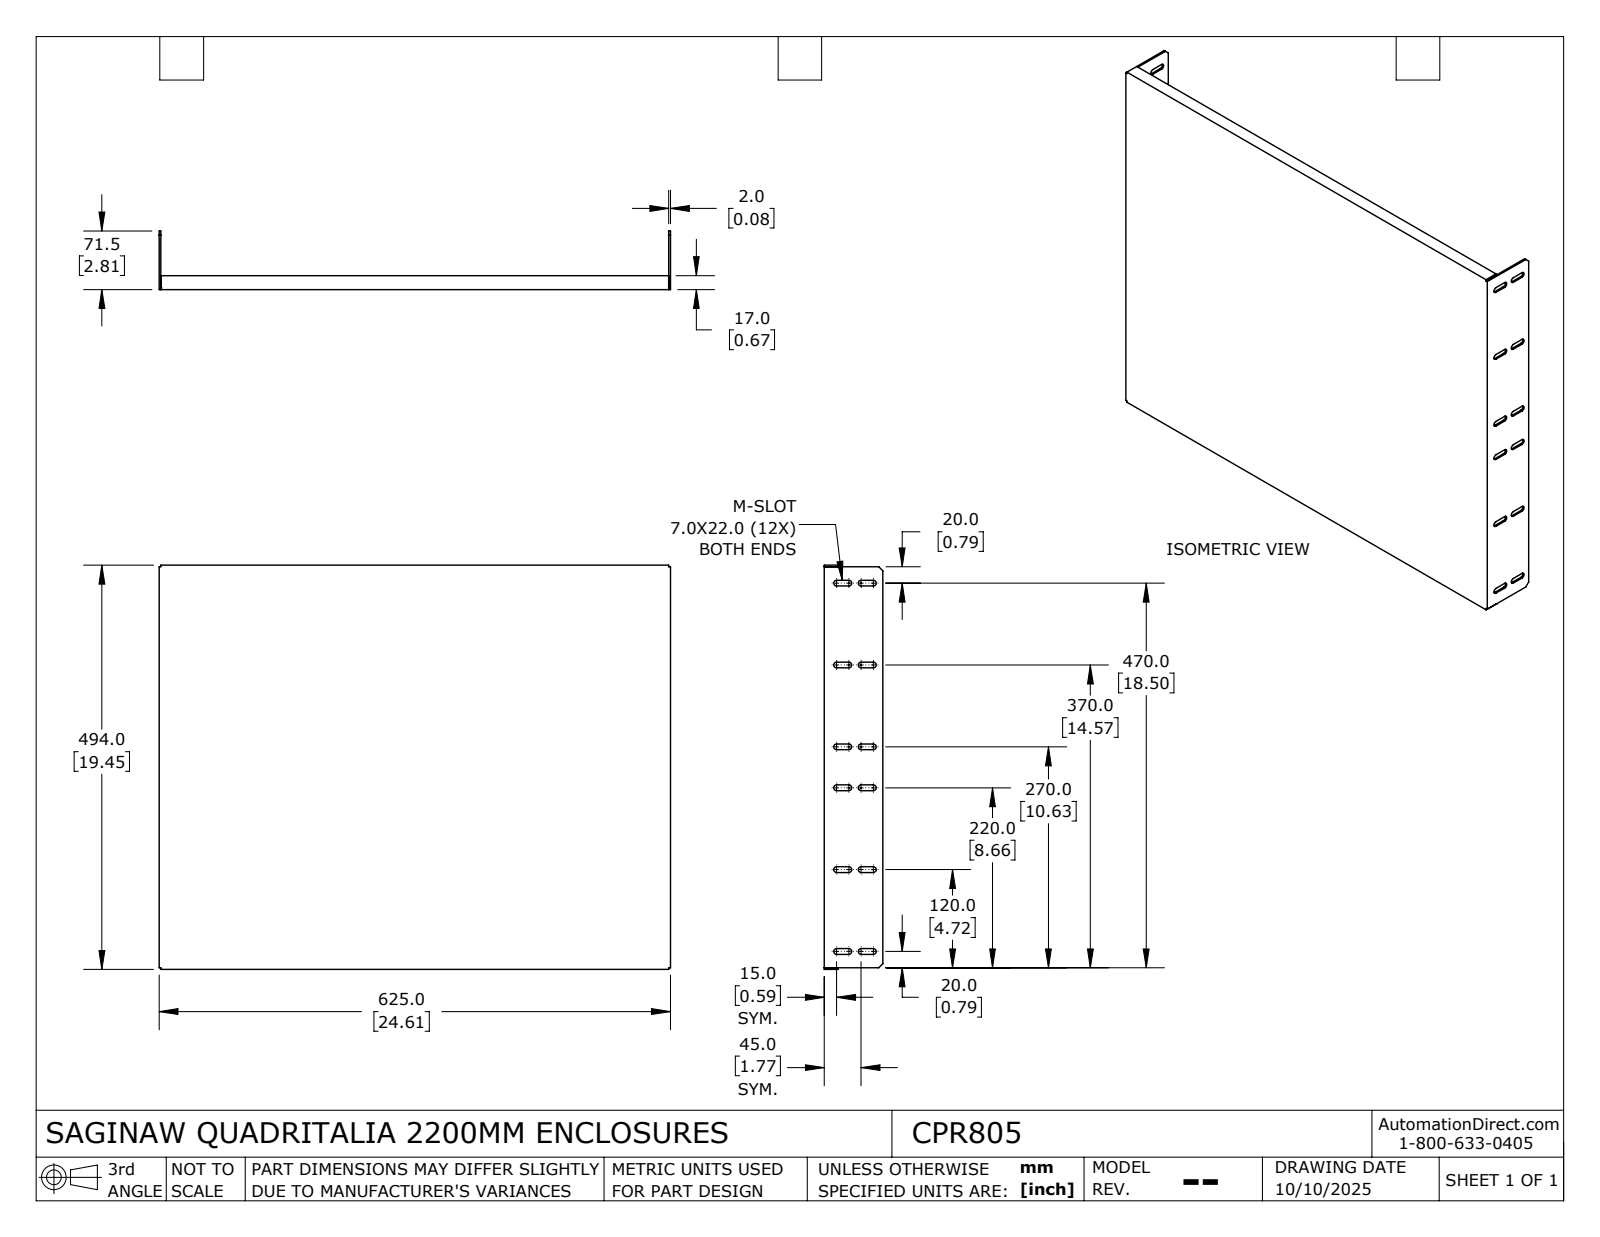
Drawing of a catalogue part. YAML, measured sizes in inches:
part_name: "CPR805_Default"
step_written_by: "SolidWorks 2024 (CONFIG_CONTROL_DESIGN)"
units: inches
bodies: {solids: 1, faces: 123, planar: 75, cylindrical: 48, other: 0}
overall_size: [24.606, 19.449, 2.815]
volume: 47.84
surface_area: 1227
partial_cylinders:
  - {radius: 0.138, count: 24}
face_to_face_distances: [0.079, 24.528, 24.606, 24.449, 19.37, 19.449, 19.291, 0.669, 0.591, 2.815]
